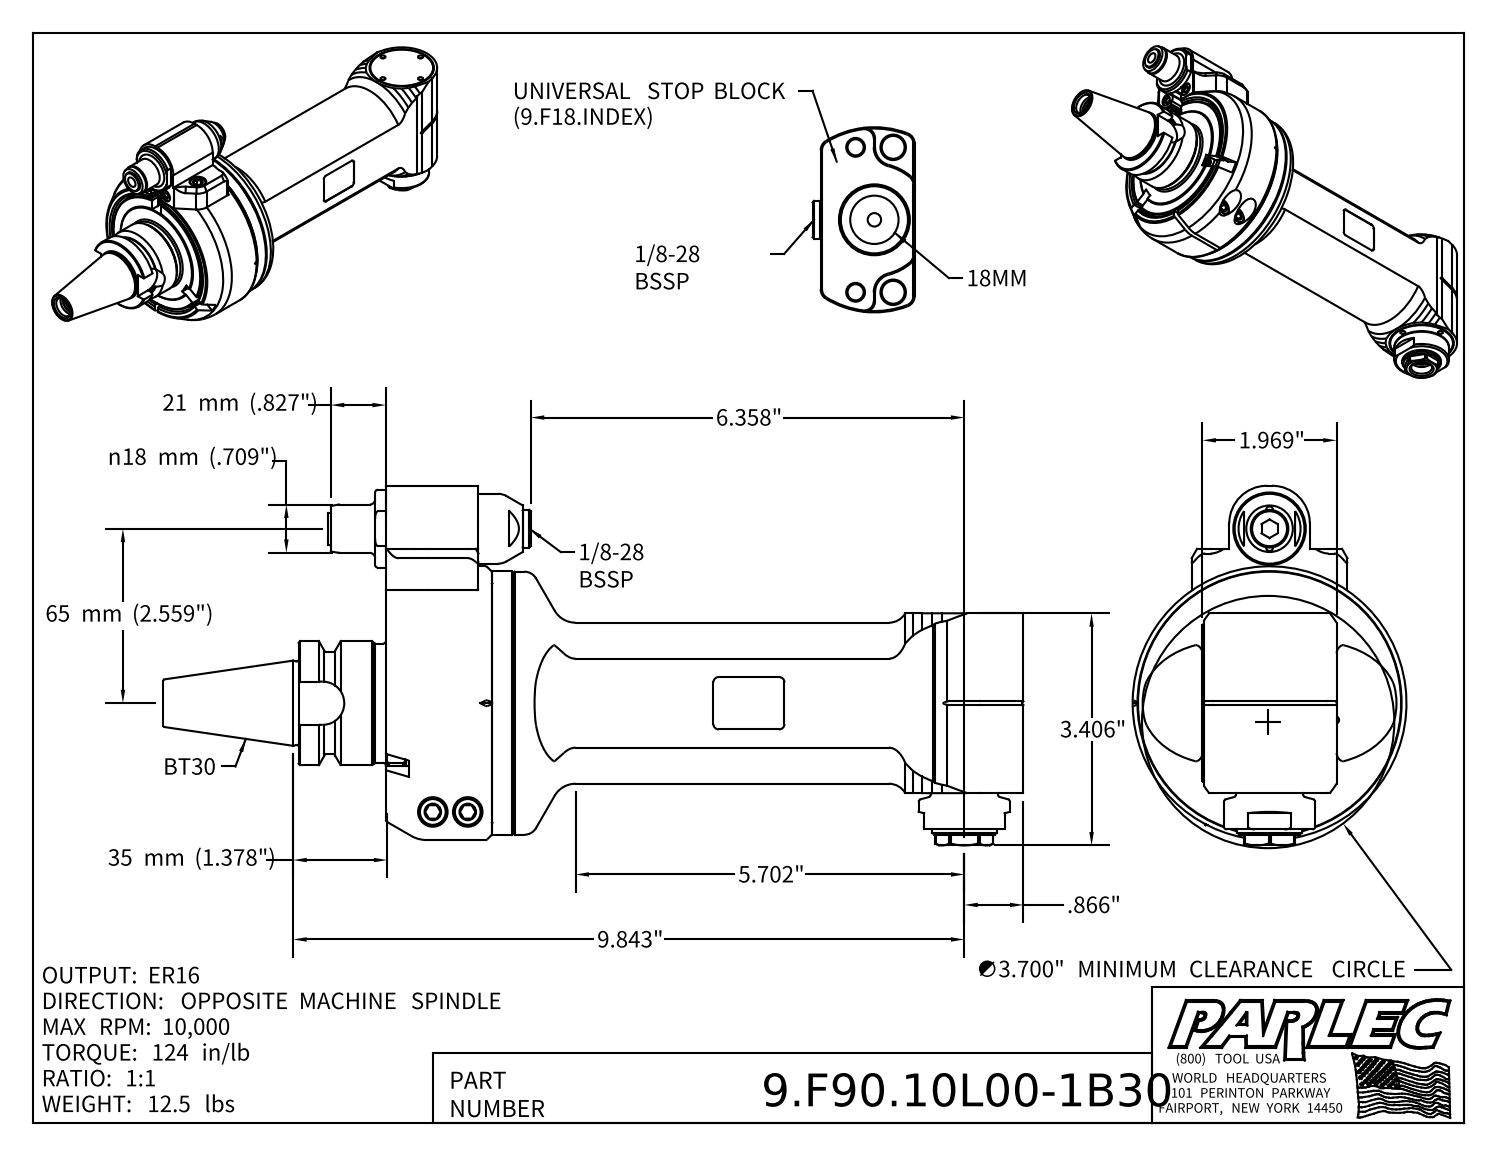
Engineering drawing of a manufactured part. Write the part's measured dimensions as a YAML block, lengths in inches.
part_name: "9.F90.10L00-1B30; 9_F90_10L00; step_9ga11c_336 (Evo, Type 1, BT30, 65mm)"
step_written_by: "Autodesk Inventor 2022 (AUTOMOTIVE_DESIGN)"
units: inches
bodies: {solids: 28, faces: 838, planar: 336, cylindrical: 238, other: 264}
overall_size: [12.614, 5.276, 4.016]
volume: 62.02
surface_area: 285.7
round_holes:
  - {diameter: 0.335, count: 20}
  - {diameter: 0.126, count: 8}
  - {diameter: 0.197, count: 7}
  - {diameter: 0.165, count: 6}
  - {diameter: 0.13, count: 4}
  - {diameter: 0.236, count: 3}
  - {diameter: 0.256, count: 3}
  - {diameter: 0.315, count: 3}
  - {diameter: 0.433, count: 3}
  - {diameter: 0.102, count: 2}
  - {diameter: 0.266, count: 2}
  - {diameter: 0.409, count: 2}
round_bosses_or_shafts:
  - {diameter: 0.394, count: 5}
  - {diameter: 0.236, count: 4}
  - {diameter: 0.157, count: 4}
  - {diameter: 0.866, count: 2}
  - {diameter: 0.709, count: 2}
  - {diameter: 0.472, count: 2}
  - {diameter: 0.197, count: 2}
  - {diameter: 0.098, count: 2}
partial_cylinders:
  - {radius: 0.039, count: 14}
  - {radius: 0.079, count: 12}
  - {radius: 0.118, count: 6}
  - {radius: 0.157, count: 4}
  - {radius: 0.016, count: 2}
  - {radius: 0.02, count: 2}
  - {radius: 0.315, count: 2}
  - {radius: 0.551, count: 2}
face_to_face_distances: [1.26, 0.02, 0.335, 1.555, 1.969, 0.276, 0.295, 0.65, 1.28, 0.197]
hole_center_spacings: [1.516, 2.144, 1.824, 3.002, 0.835, 2.651, 2.914, 3.031]
